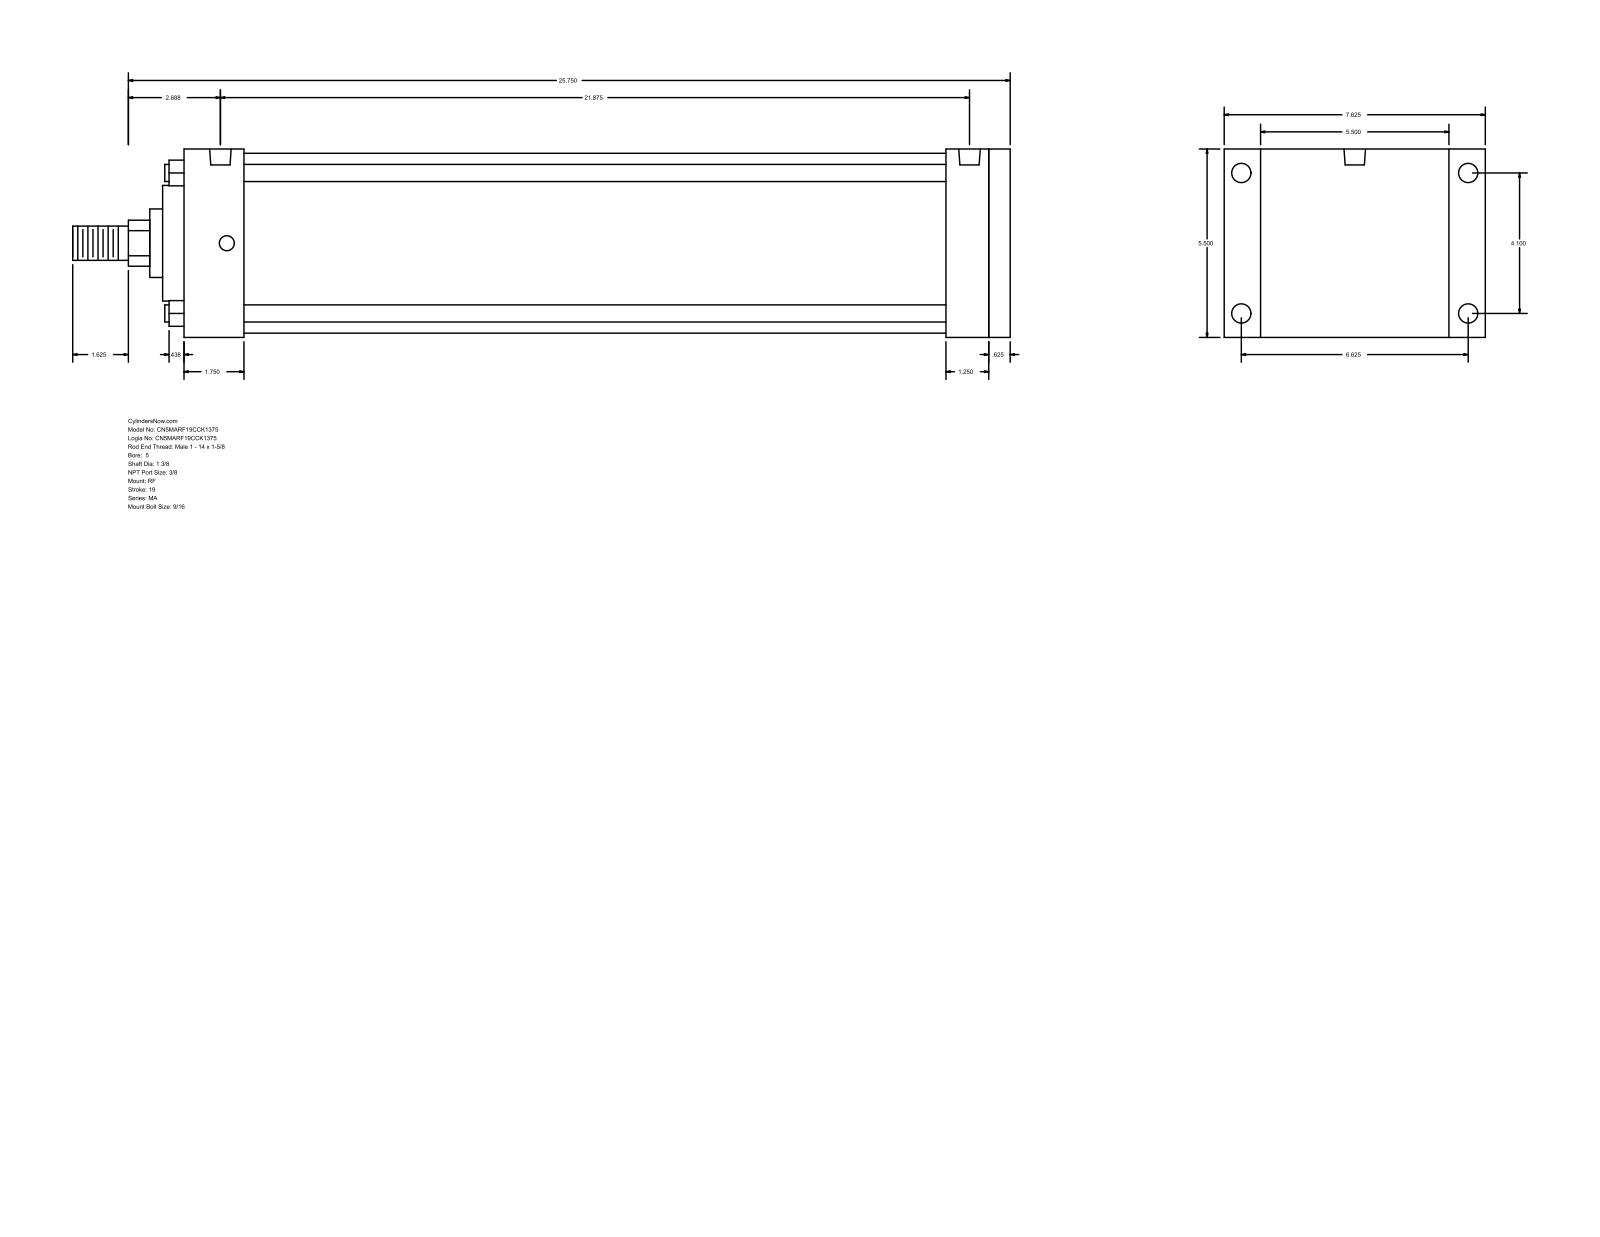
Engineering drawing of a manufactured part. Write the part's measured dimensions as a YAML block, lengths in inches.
part_name: "MA_RF__0500_1.375"
step_written_by: "GSSL Pune (CONFIG_CONTROL_DESIGN)"
units: inches
bodies: {solids: 0, faces: 94, planar: 65, cylindrical: 29, other: 0}
overall_size: [27.375, 7.625, 5.5]
round_holes:
  - {diameter: 0.437, count: 4}
  - {diameter: 0.563, count: 4}
  - {diameter: 0.627, count: 2}
round_bosses_or_shafts:
  - {diameter: 0.5, count: 4}
  - {diameter: 5.25, count: 1}
  - {diameter: 3.375, count: 1}
  - {diameter: 2, count: 1}
  - {diameter: 1.375, count: 1}
  - {diameter: 1, count: 1}
partial_cylinders:
  - {radius: 0.672, count: 1}
face_to_face_distances: [5.5, 24.125, 0.625, 23.5, 1.75, 21.75, 22.375, 22.25, 20.5, 1.25]
hole_center_spacings: [0.188, 4.1, 6.625, 7.791, 21.5, 21.687, 21.875]
